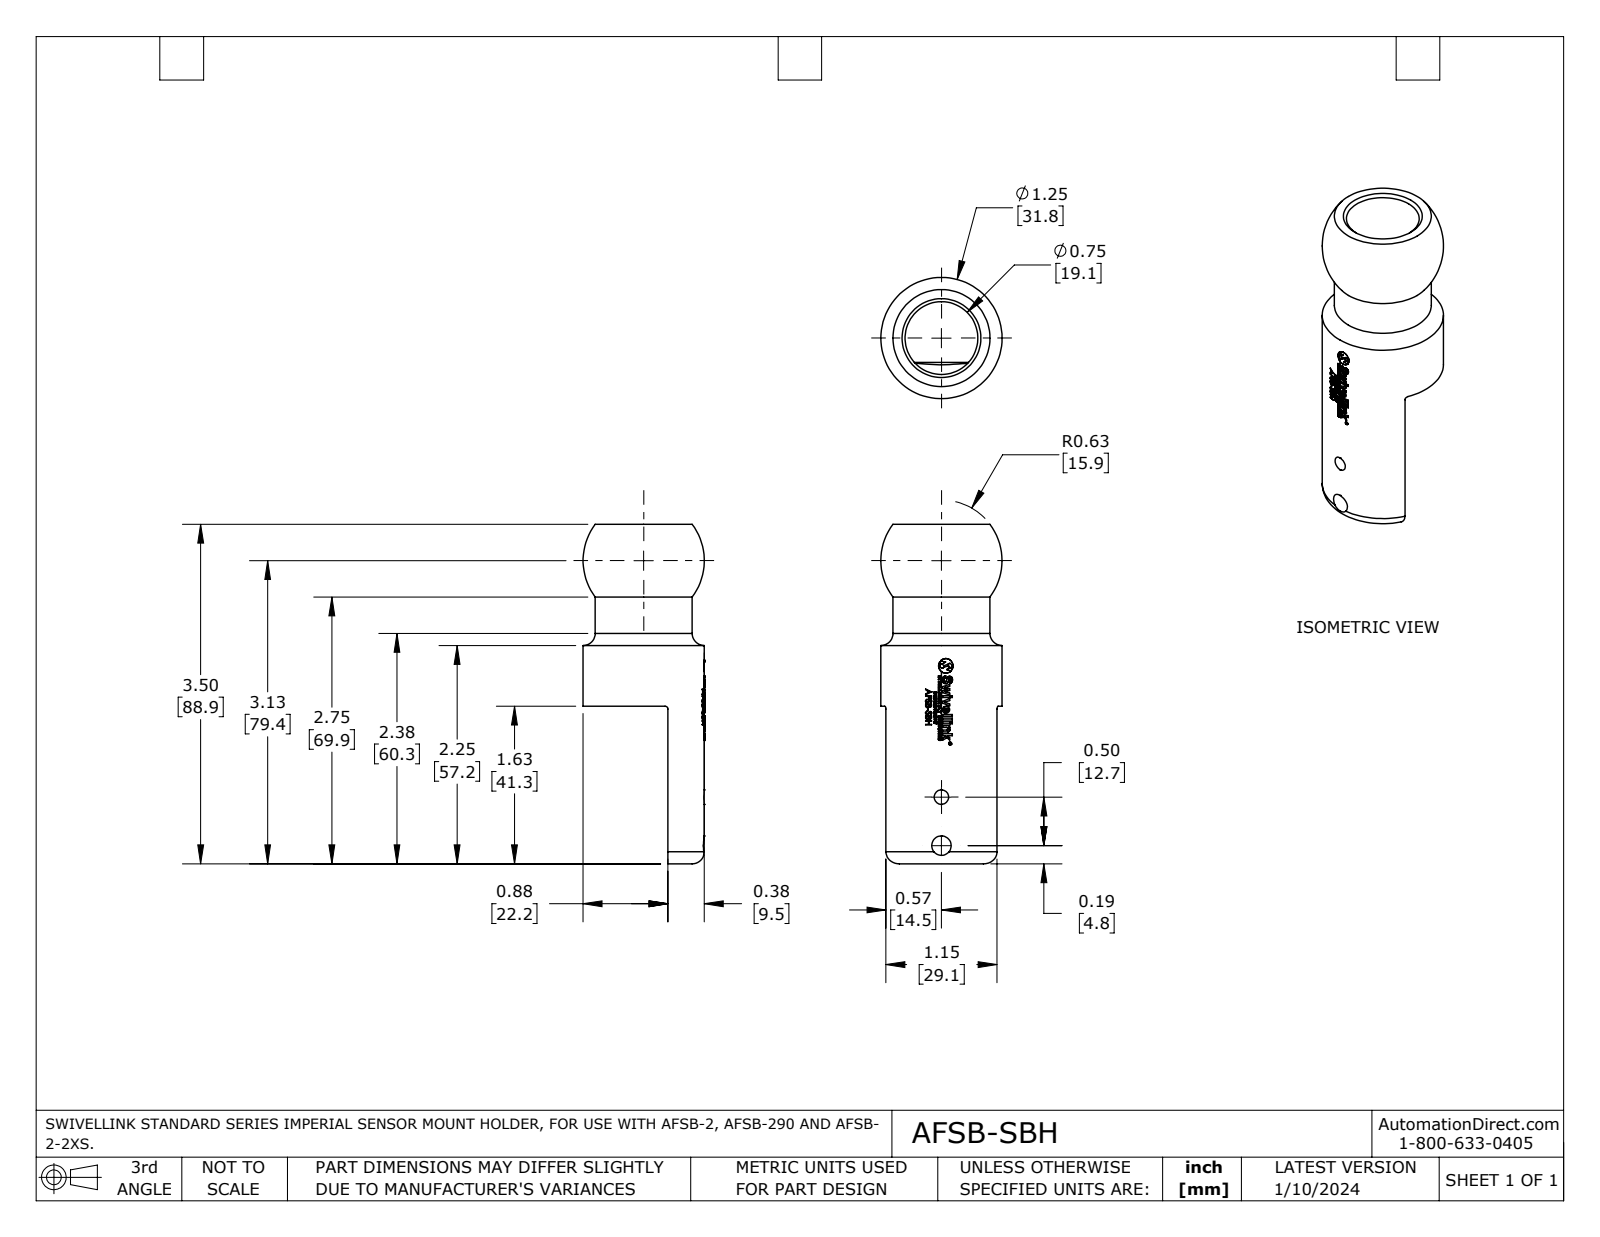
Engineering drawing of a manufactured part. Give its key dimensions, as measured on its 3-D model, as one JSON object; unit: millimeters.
{"part_name": "AFSB-SBH", "step_written_by": "SolidWorks 2023 (AUTOMOTIVE_DESIGN)", "units": "millimeters", "bodies": {"solids": 1, "faces": 115, "planar": 6, "cylindrical": 96, "other": 13}, "overall_size": [88.9, 31.8, 31.8], "volume_mm3": 26250, "surface_area_mm2": 11140, "round_holes": [[3.8, 1], [5.1, 1], [19.1, 1]], "round_bosses_or_shafts": [[31.8, 1], [25.4, 1]], "partial_cylinders_radius": [[0.8, 1]], "face_to_face_distances": [47.6, 88.9, 41.3], "hole_center_spacings": [12.7]}
